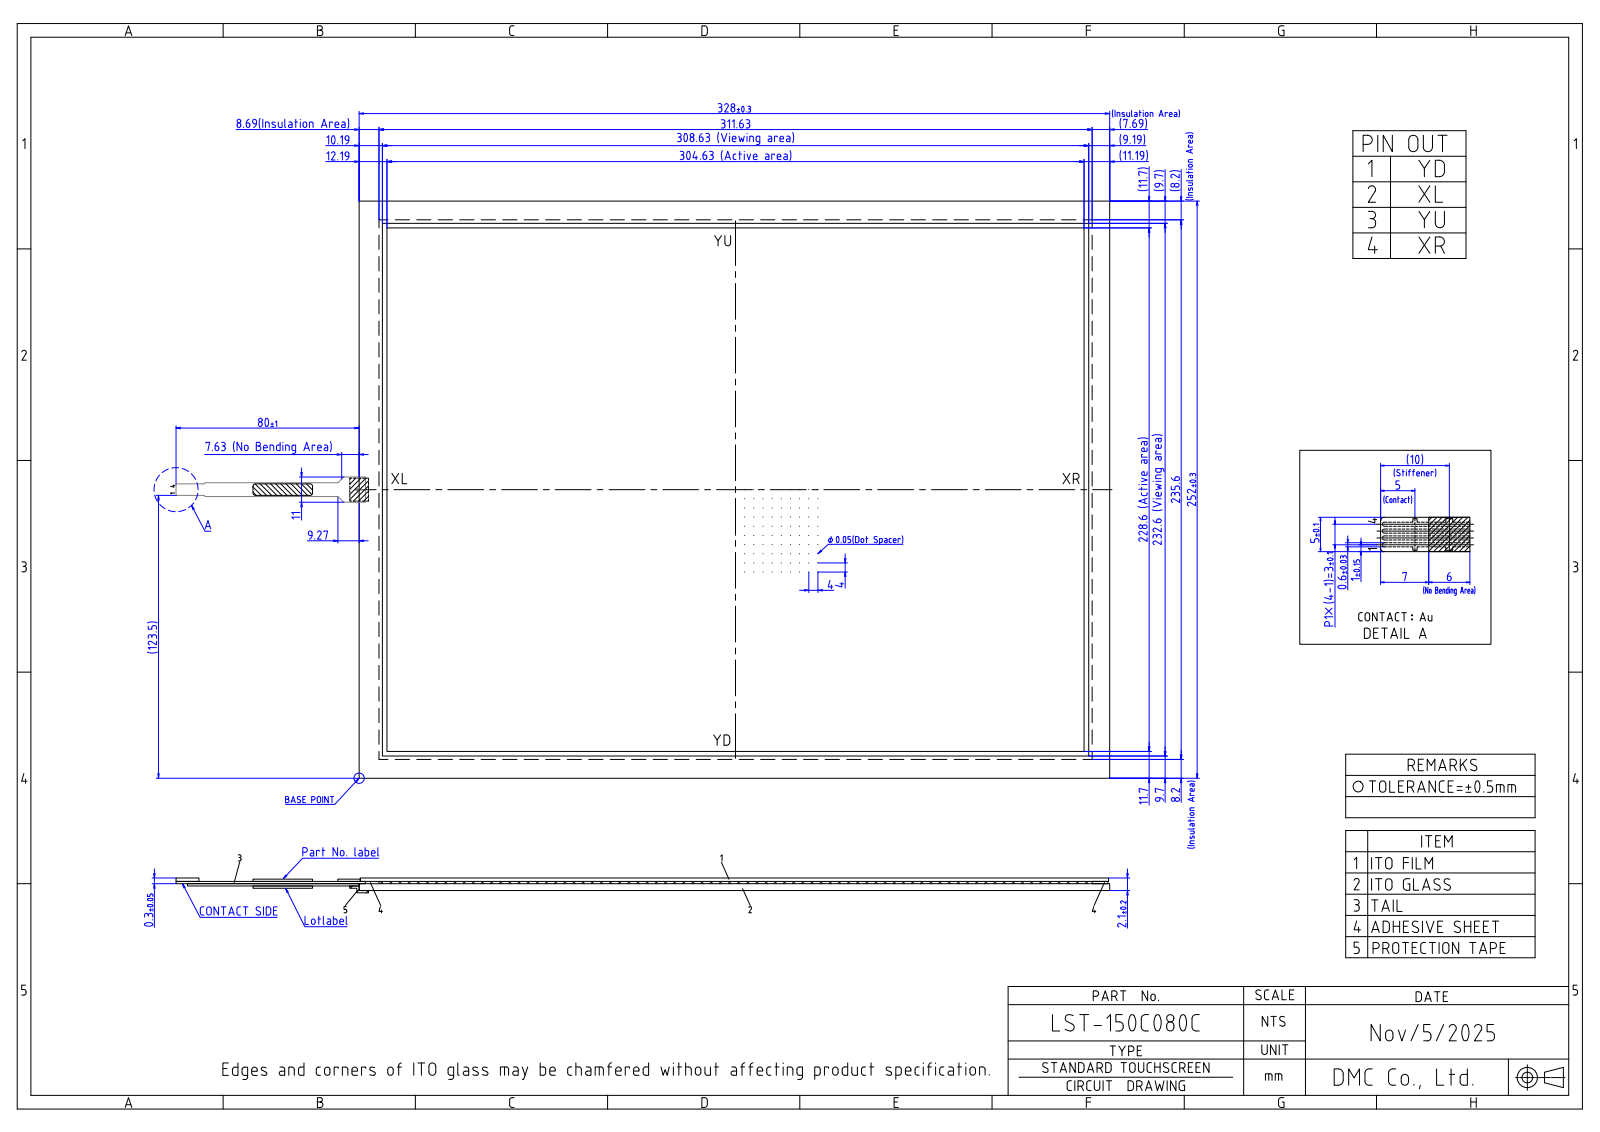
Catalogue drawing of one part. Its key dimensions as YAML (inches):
part_name: "LST-150C080C"
step_written_by: "Autodesk Inventor 2020 (CONFIG_CONTROL_DESIGN)"
units: inches
bodies: {solids: 2, faces: 52, planar: 46, cylindrical: 6, other: 0}
overall_size: [18.646, 13.89, 0.102]
volume: 10.58
surface_area: 261.9
partial_cylinders:
  - {radius: 0.012, count: 4}
  - {radius: 0.02, count: 2}
face_to_face_distances: [0.083, 0.079, 9.921, 12.913, 0.087, 0.091, 0.382, 9.539, 0.461, 9.461]
